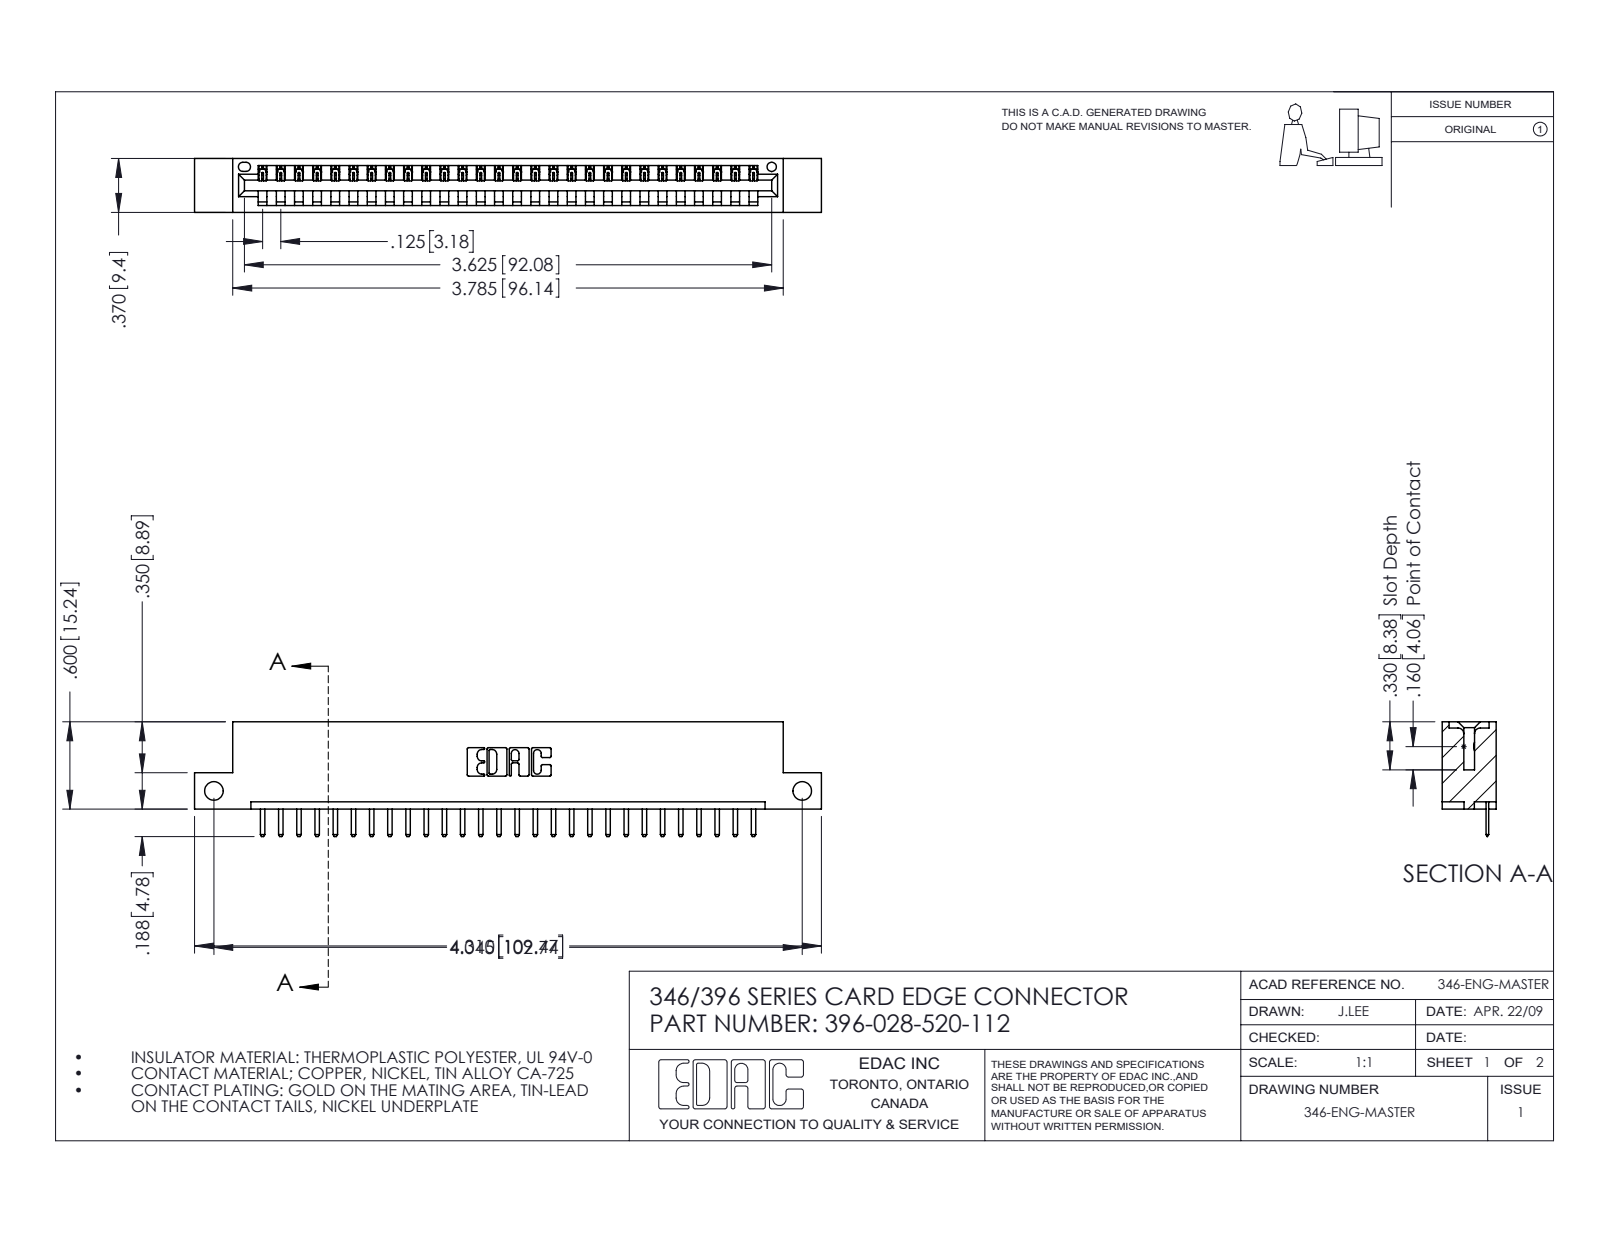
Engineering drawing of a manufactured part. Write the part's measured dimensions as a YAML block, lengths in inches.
part_name: "345-292-001_345-293-120; 396-028-520-112; 346 Part_Flush Mounting Lugs - Side Mount"
step_written_by: "SolidWorks 2016 (CONFIG_CONTROL_DESIGN)"
units: inches
bodies: {solids: 29, faces: 1858, planar: 1252, cylindrical: 606, other: 0}
overall_size: [4.31, 0.788, 0.37]
volume: 0.623
surface_area: 18.91
round_holes:
  - {diameter: 0.128, count: 2}
  - {diameter: 0.064, count: 1}
partial_cylinders:
  - {radius: 0.01, count: 58}
  - {radius: 0.006, count: 56}
  - {radius: 0.01, count: 22}
  - {radius: 0.007, count: 6}
  - {radius: 0.031, count: 6}
  - {radius: 0.026, count: 3}
  - {radius: 0.031, count: 2}
  - {radius: 0.04, count: 2}
face_to_face_distances: [0.048, 0.322, 0.37, 0.25, 0.148, 0.222, 0.1, 0.174, 0.072, 0.298]
hole_center_spacings: [4.045]
